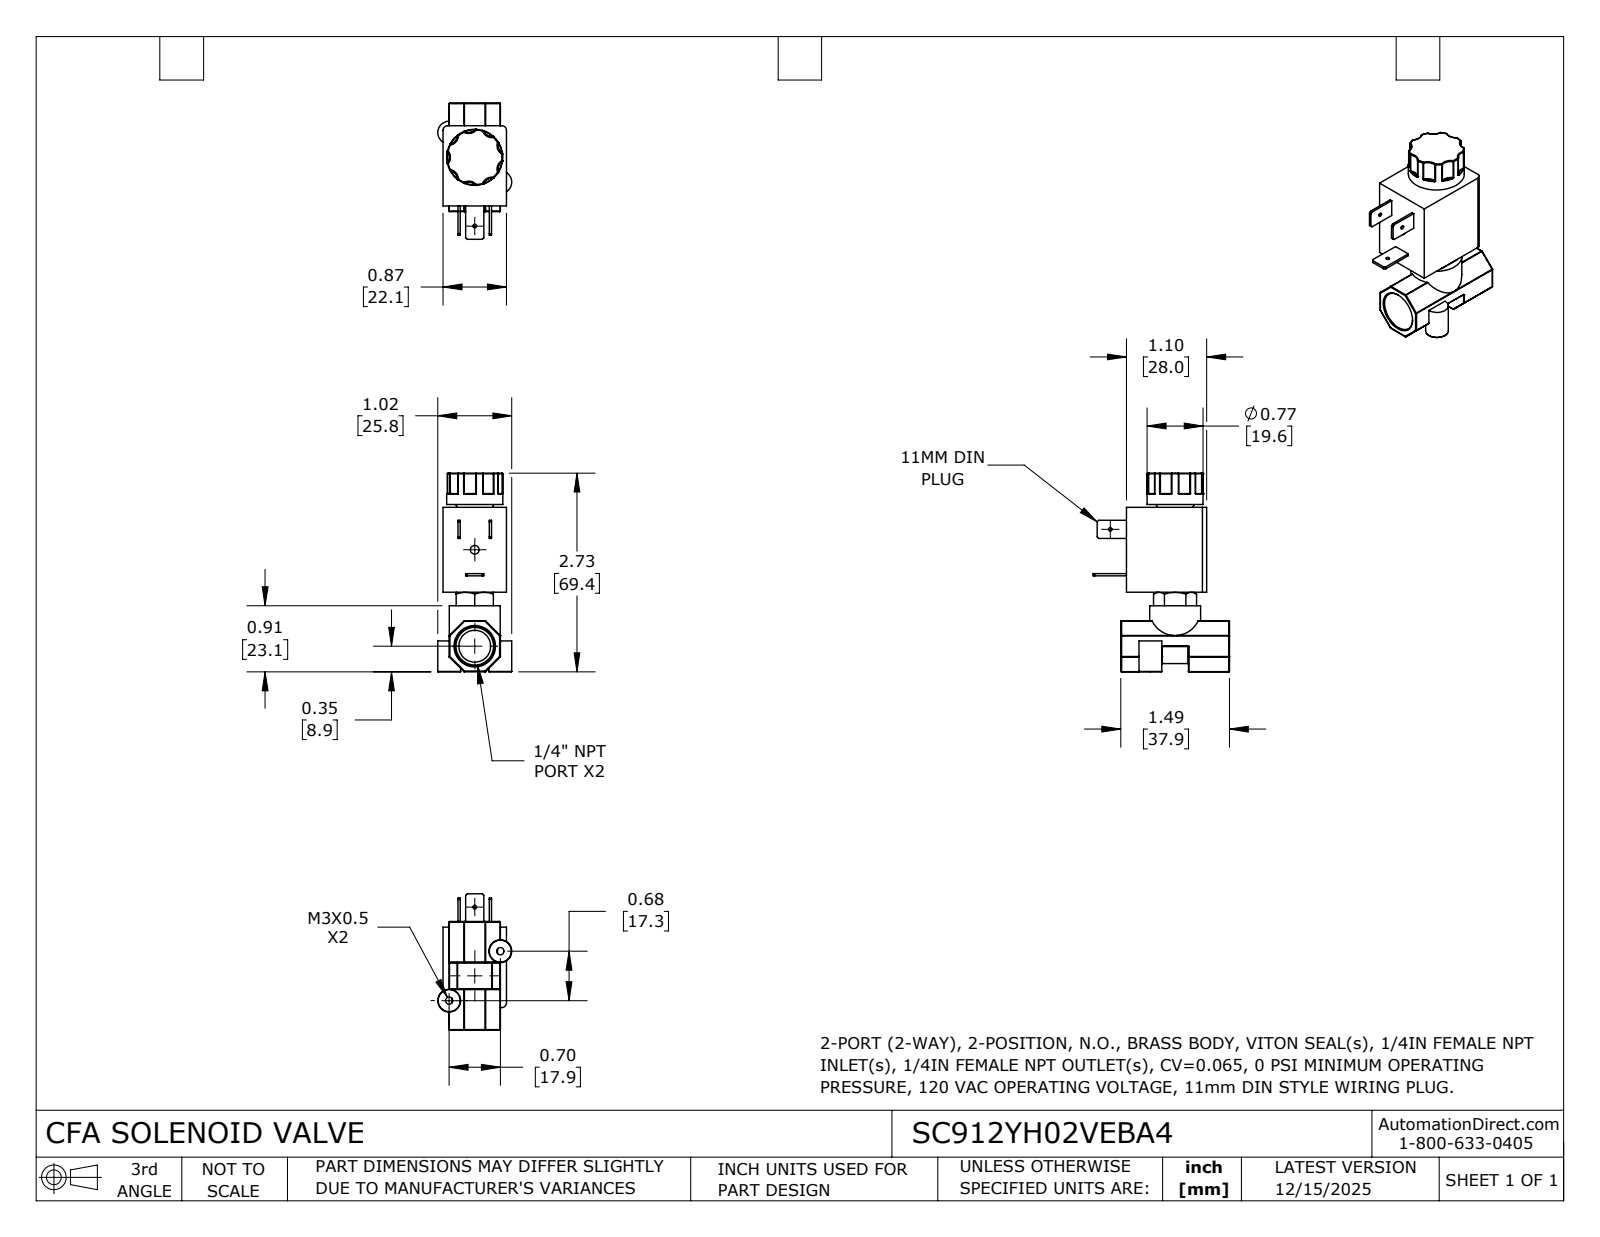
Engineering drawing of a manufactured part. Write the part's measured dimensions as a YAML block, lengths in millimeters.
part_name: "SC912YH02VEBA4"
step_written_by: "SolidWorks 2024 (CONFIG_CONTROL_DESIGN)"
units: millimeters
bodies: {solids: 1, faces: 350, planar: 74, cylindrical: 107, other: 169}
overall_size: [69.4, 47.6, 25.8]
volume: 29870
surface_area: 10510
round_holes:
  - {diameter: 1.3, count: 2}
  - {diameter: 2.5, count: 2}
  - {diameter: 3, count: 1}
  - {diameter: 11.1, count: 1}
round_bosses_or_shafts:
  - {diameter: 8, count: 2}
  - {diameter: 19.6, count: 1}
  - {diameter: 17.8, count: 1}
partial_cylinders:
  - {radius: 0.3, count: 42}
  - {radius: 0.1, count: 14}
  - {radius: 3.4, count: 7}
  - {radius: 1.5, count: 2}
  - {radius: 3.4, count: 2}
  - {radius: 6, count: 1}
  - {radius: 8, count: 1}
face_to_face_distances: [22.1, 17.9, 28, 29.6, 2.1, 20, 27.8, 57.4, 69.4, 41.6]
hole_center_spacings: [17.8, 24.9, 33.7, 33.9]
